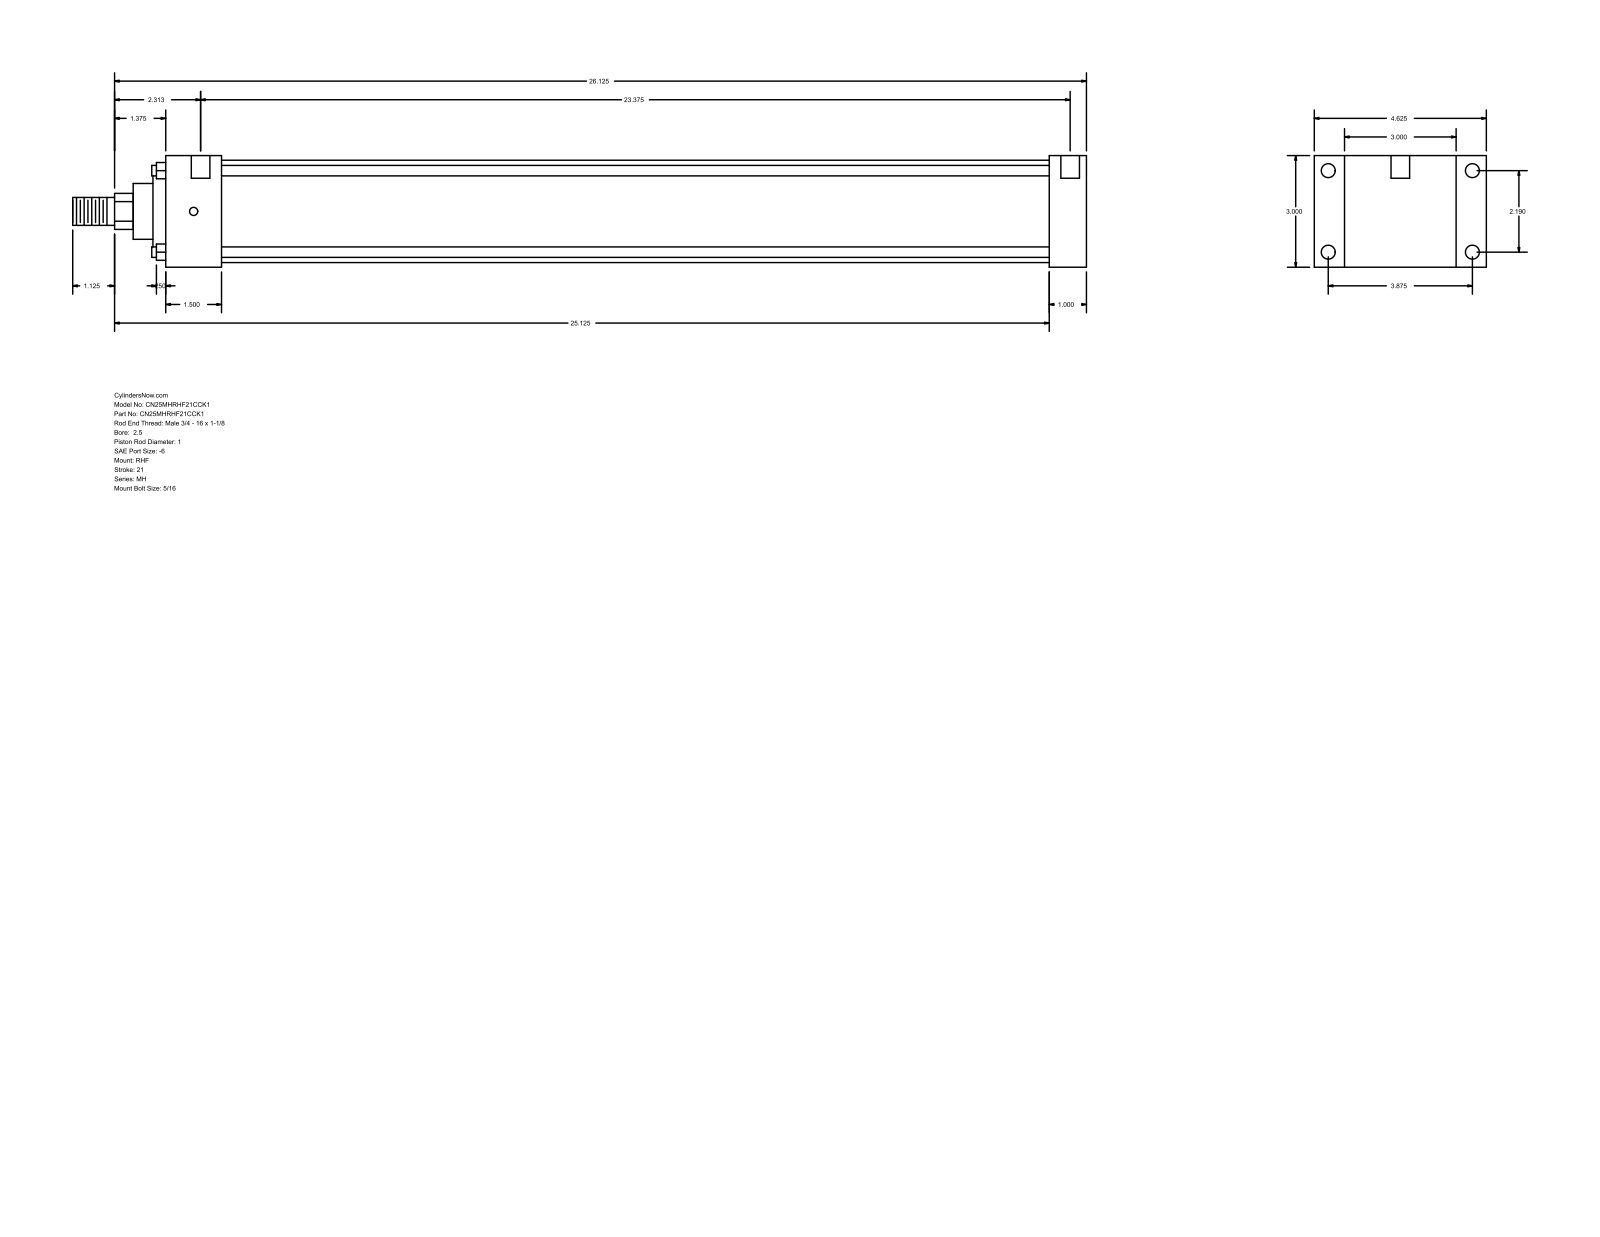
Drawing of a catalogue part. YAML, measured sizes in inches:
part_name: "MH_RHF__0250_1"
step_written_by: "GSSL Pune (CONFIG_CONTROL_DESIGN)"
units: inches
bodies: {solids: 0, faces: 90, planar: 61, cylindrical: 29, other: 0}
overall_size: [27.25, 4.625, 3]
round_holes:
  - {diameter: 0.219, count: 4}
  - {diameter: 0.375, count: 4}
  - {diameter: 0.5, count: 2}
round_bosses_or_shafts:
  - {diameter: 0.281, count: 4}
  - {diameter: 2.75, count: 1}
  - {diameter: 2.375, count: 1}
  - {diameter: 1.5, count: 1}
  - {diameter: 1, count: 1}
  - {diameter: 0.75, count: 1}
partial_cylinders:
  - {radius: 0.484, count: 1}
face_to_face_distances: [3, 1, 0.813, 3.813, 23.75, 24.75, 4.625, 1.5, 22.25, 23.25]
hole_center_spacings: [2.19, 3.875, 4.451, 23.687, 0.125, 0.187, 23.375, 23.5]
